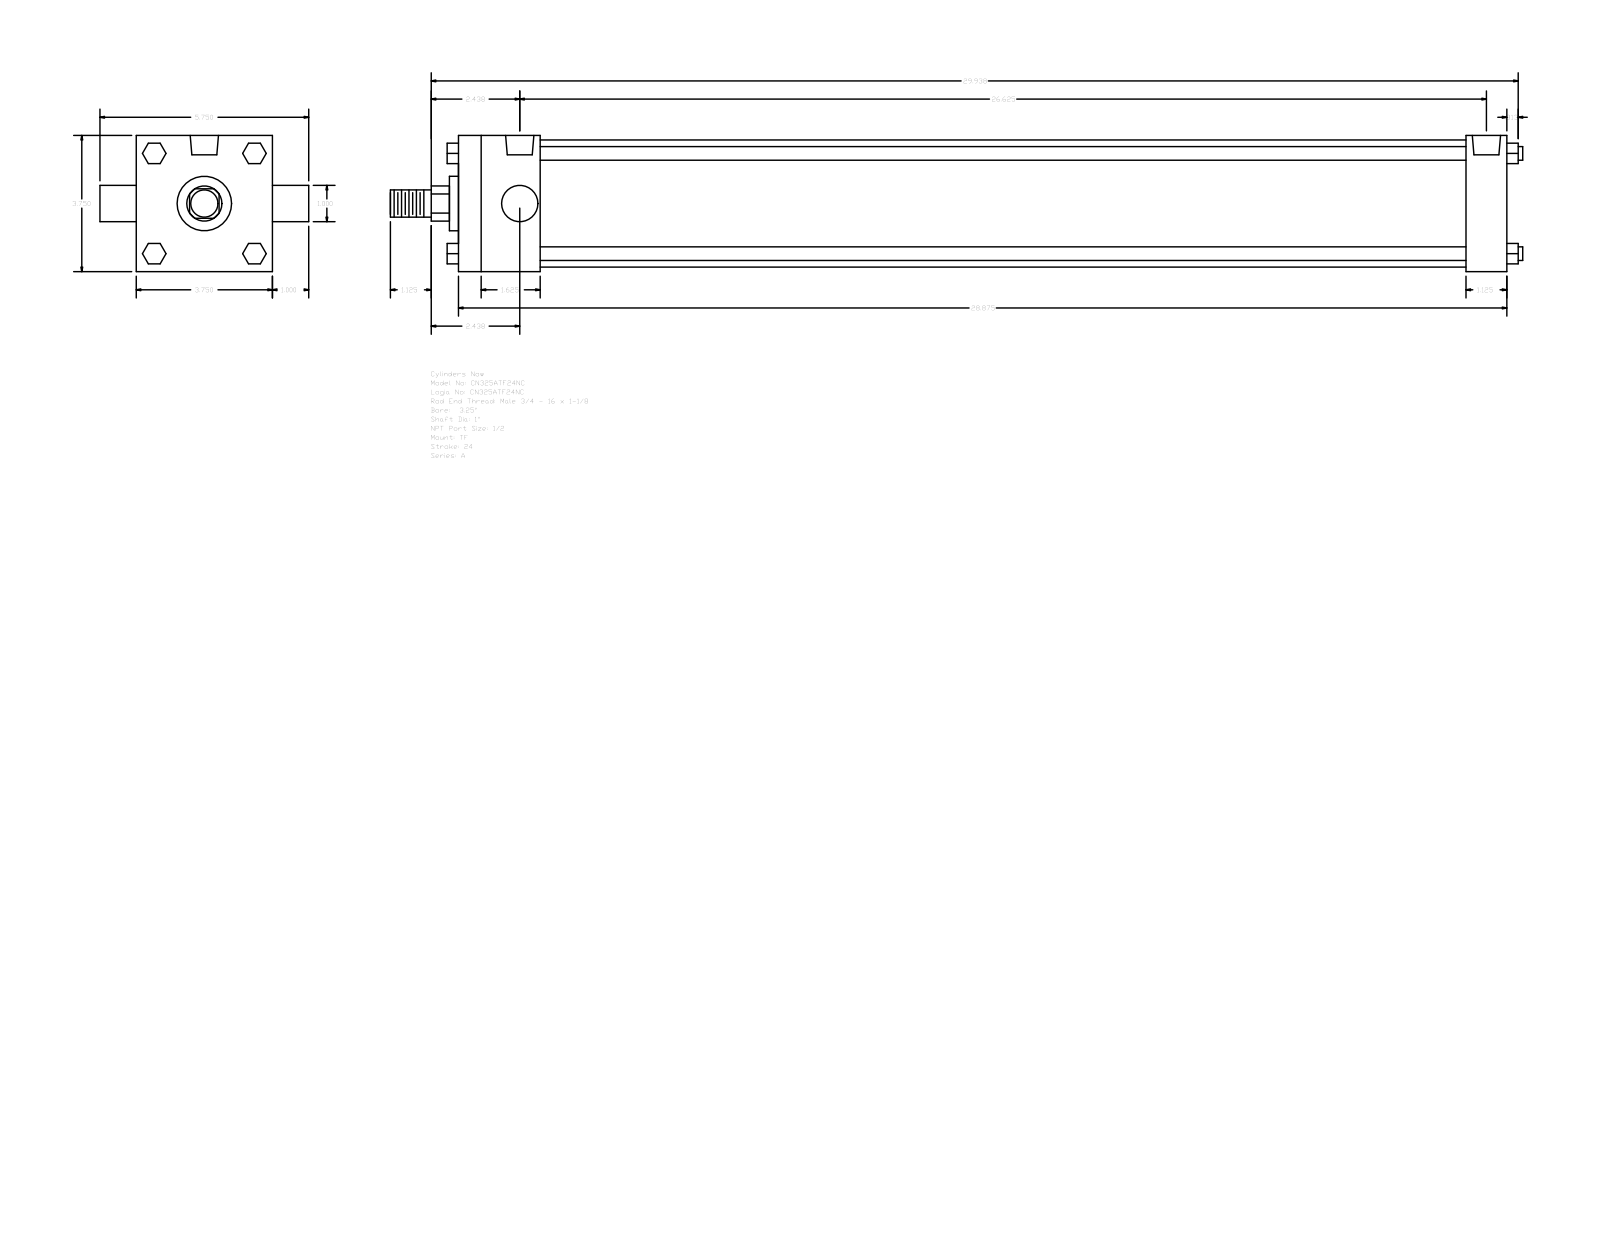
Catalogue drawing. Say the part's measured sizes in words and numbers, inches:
The part is named "A_TF__0325_1". Its 3-D file was written by "GSSL Pune (CONFIG_CONTROL_DESIGN)". It is 0 solids with 120 faces: 92 planar, 28 cylindrical and 0 other. Overall it measures 31.187 by 5.75 by 3.75 inches. Round holes: 3 of diameter 0.344, 2 of diameter 0.778. Round bosses or shafts: 4 of diameter 0.375, 2 of diameter 1, 1 of diameter 3.5, 1 of diameter 1.5, 1 of diameter 0.75. Partial cylindrical surfaces (rounded edges, fillets, slot ends): 1 of radius 0.484. The main face-to-face distances are 3.75, 28.875, 2.25, 27.75, 25.5, 26.625, 1.125, 0.562, 1.38, 2.39. The hole center spacings are 0.125, 26.5, 26.375, 26.625.
